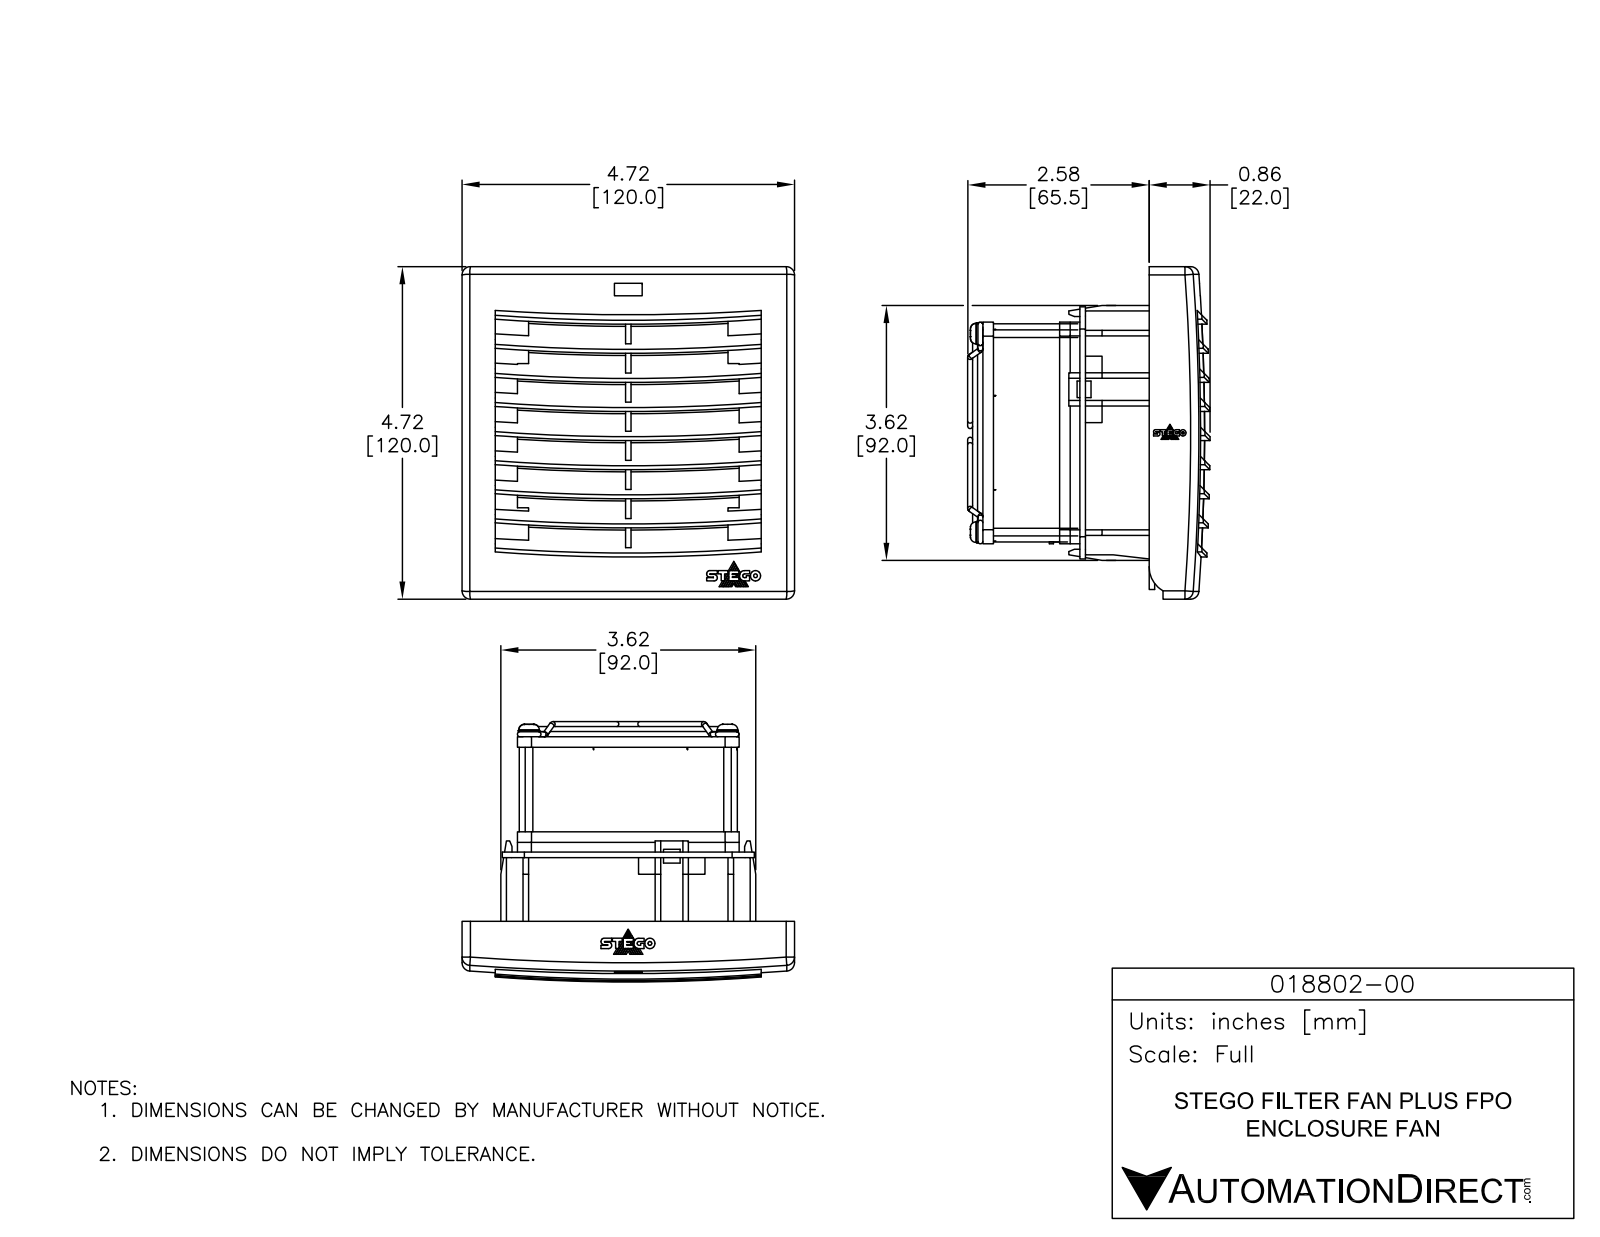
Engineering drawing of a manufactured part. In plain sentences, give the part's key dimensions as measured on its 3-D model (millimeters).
The part is named "018802-00". Its 3-D file was written by "SolidWorks 2018 (AUTOMOTIVE_DESIGN)". It is 1 solid with 506 faces: 293 planar, 205 cylindrical and 8 other. Overall it measures 120 by 120 by 95 millimeters. Its volume is 332 200 cubic millimeters and its surface area 143 500 square millimeters. Round holes: 4 of diameter 5.5, 1 of diameter 17, 1 of diameter 29.3, 1 of diameter 41.5, 1 of diameter 50.7, 1 of diameter 53.8, 1 of diameter 63.4, 1 of diameter 68, 1 of diameter 78.2. Round bosses or shafts: 1 of diameter 67.6, 1 of diameter 57.8, 1 of diameter 54.9, 1 of diameter 45.5, 1 of diameter 33.3, 1 of diameter 23.8, 1 of diameter 21. Partial cylindrical surfaces (rounded edges, fillets, slot ends): 15 of radius 219.2, 5 of radius 33.3, 4 of radius 2.5, 4 of radius 3, 1 of radius 13.7, 1 of radius 19, 1 of radius 21.1, 1 of radius 43.6. The main face-to-face distances are 1.5, 8, 3, 2.3, 89.7, 16.1, 6.1, 9.5, 14, 16.3. The hole center spacings are 52.9, 74.8, 105.8.
